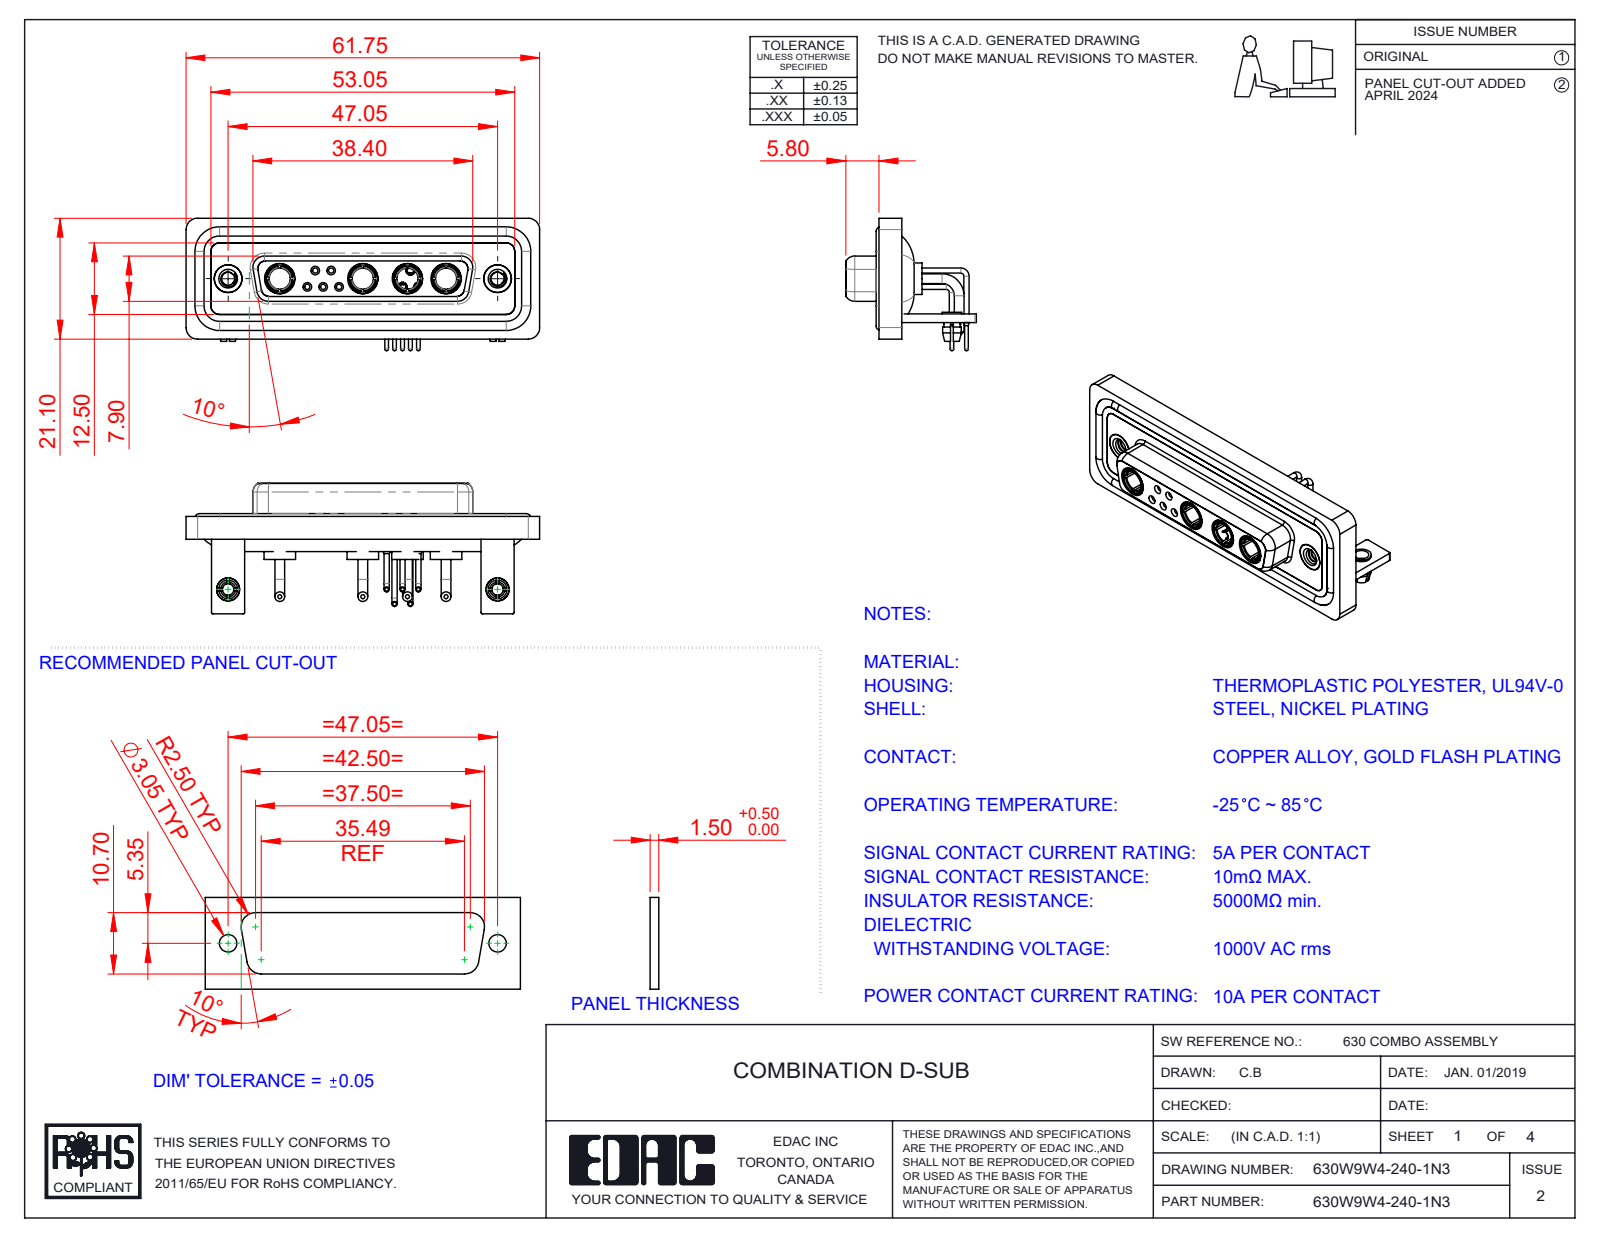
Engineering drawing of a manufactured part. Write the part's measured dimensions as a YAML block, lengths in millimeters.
part_name: "630Combo Shell Rear_25 Contacts; Power Socket_10A RA; 630Combo Shell Front_25 Contacts; 630Combo Contact Row 2_50 Contacts (+7 more)"
step_written_by: "SolidWorks 2023 (CONFIG_CONTROL_DESIGN)"
units: millimeters
bodies: {solids: 24, faces: 1103, planar: 364, cylindrical: 459, other: 280}
overall_size: [61.75, 23.12, 22.8]
volume: 8623
surface_area: 14790
round_holes:
  - {diameter: 2, count: 7}
  - {diameter: 4.85, count: 6}
  - {diameter: 0.9, count: 5}
  - {diameter: 1.1, count: 5}
  - {diameter: 1.5, count: 5}
  - {diameter: 3.7, count: 4}
  - {diameter: 5.3, count: 4}
  - {diameter: 1.6, count: 3}
  - {diameter: 1.7, count: 2}
  - {diameter: 2.26, count: 2}
  - {diameter: 2.5, count: 2}
  - {diameter: 3.2, count: 2}
round_bosses_or_shafts:
  - {diameter: 0.9, count: 10}
  - {diameter: 1.6, count: 9}
  - {diameter: 1.7, count: 8}
  - {diameter: 2, count: 5}
  - {diameter: 1.5, count: 5}
  - {diameter: 0.65, count: 5}
  - {diameter: 5.5, count: 4}
  - {diameter: 5.2, count: 4}
partial_cylinders:
  - {radius: 2, count: 19}
  - {radius: 1.5, count: 18}
  - {radius: 0.25, count: 16}
  - {radius: 1.35, count: 8}
  - {radius: 1.6, count: 8}
  - {radius: 0.5, count: 5}
  - {radius: 0.6, count: 4}
  - {radius: 0.65, count: 4}
face_to_face_distances: [0.4, 1.8, 2.9, 1.5, 3.7, 4.1, 1.1, 1.4, 1.6, 2.5]
hole_center_spacings: [3.16, 2.77, 5.04, 13.85, 11.08, 12.79, 15.5, 5.54]
